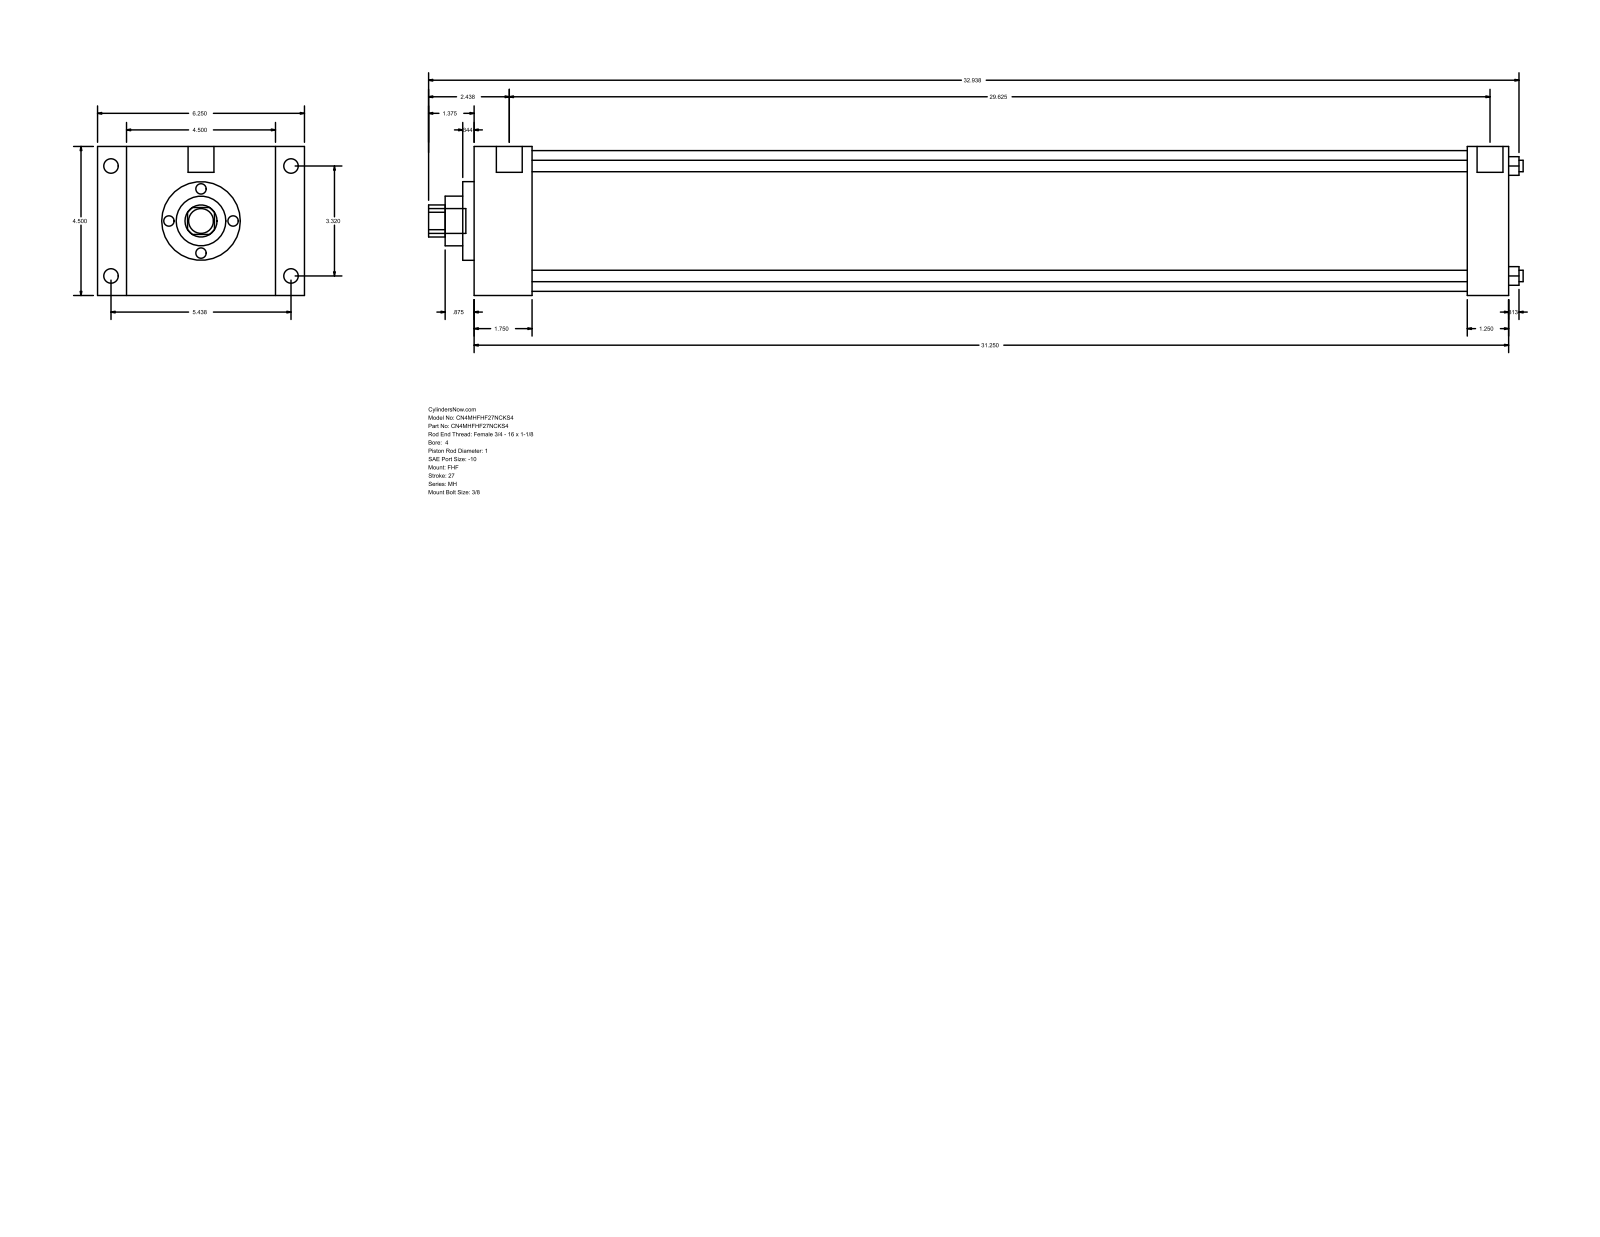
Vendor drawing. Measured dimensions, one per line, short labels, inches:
name: MH_FHF__0400_1
written by: GSSL Pune (CONFIG_CONTROL_DESIGN)
unit: in
bodies: 0 solids, 90 faces (61 planar, 29 cylindrical, 0 other)
size: 33.063 × 6.25 × 4.5
holes: 4× ⌀0.345, 1× ⌀1, 1× ⌀1.5, 1× ⌀2.375, 1× ⌀4.25
bosses: 4× ⌀0.438, 4× ⌀0.344, 2× ⌀0.781, 1× ⌀0.75
rounds: 1× R0.484
face distances: 4.5, 31.25, 1.75, 29.5, 0.875, 5.375, 6.25, 30, 28.25, 1.25
hole spacings: 2.347, 3.32, 4.695
